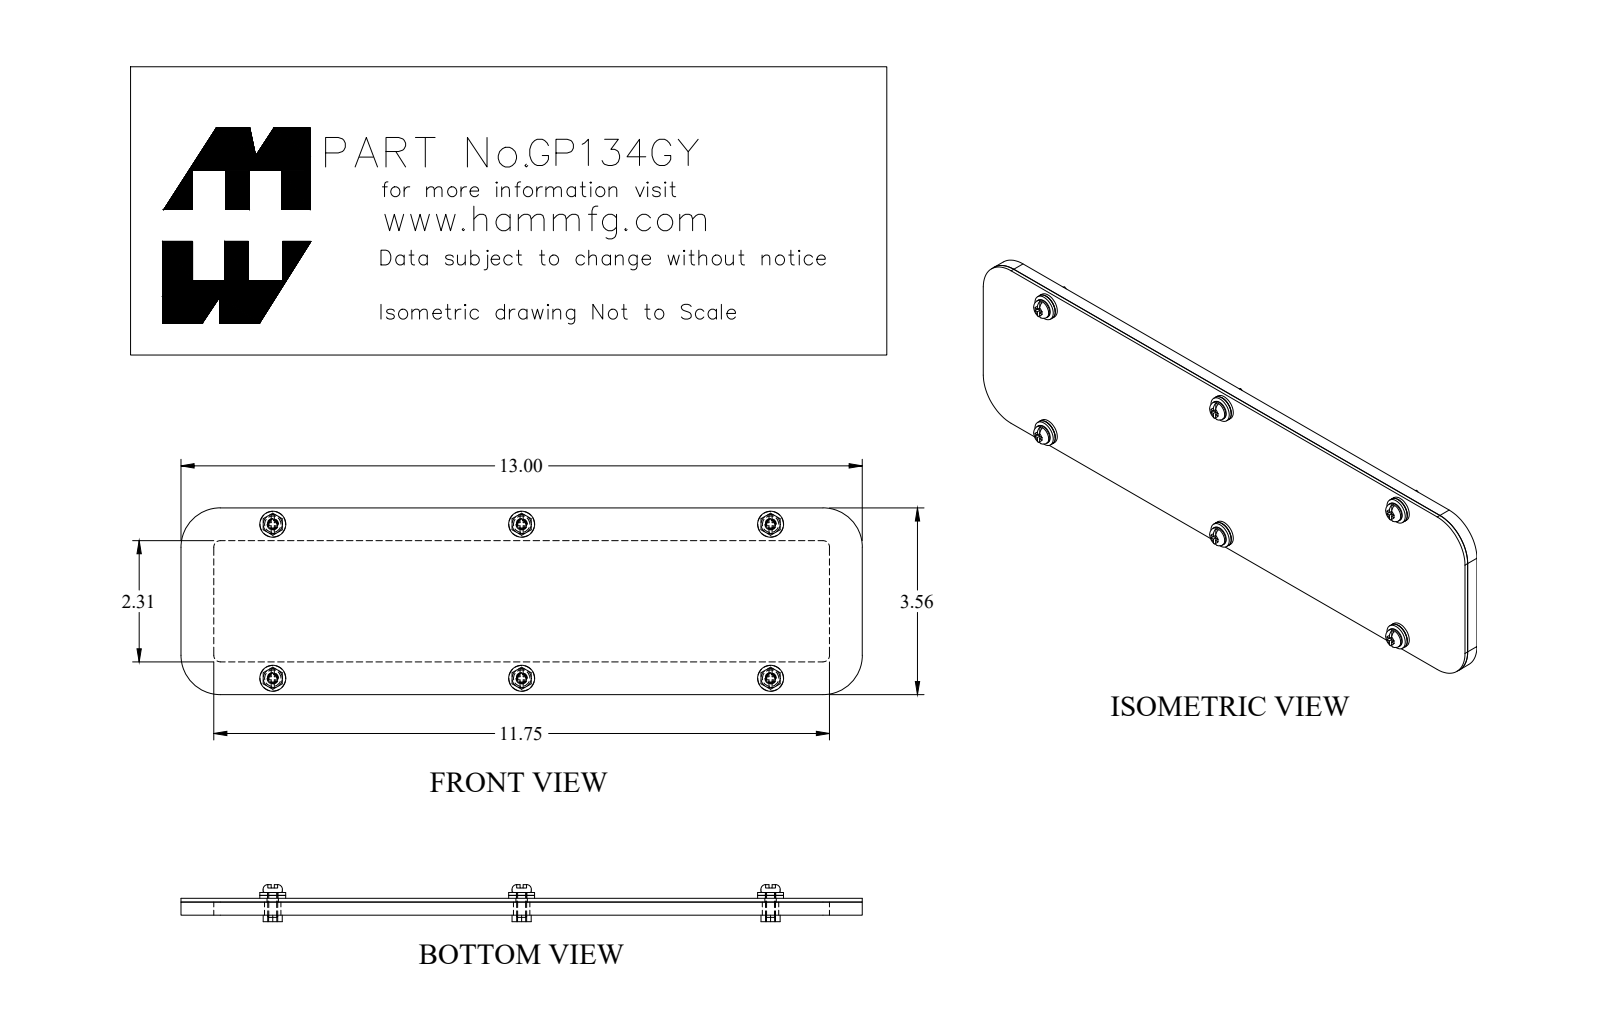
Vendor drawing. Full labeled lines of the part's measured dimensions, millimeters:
Part name (STEP PRODUCT): GP134GY
STEP written by: SolidWorks 2018 (AUTOMOTIVE_DESIGN)
Units: millimetres
Bodies: 20 solids, 346 faces (190 planar, 120 cylindrical, 36 other)
Overall size (bounding box): 330.2 × 90.5 × 18
Volume: 133 800 mm³ · Surface area: 100 900 mm²
Round holes (diameter × count): ⌀4 ×6, ⌀5 ×6, ⌀5.5 ×6, ⌀8 ×6
Round bosses / shafts (diameter × count): ⌀12.5 ×6, ⌀12.4 ×6, ⌀9.3 ×6, ⌀4.8 ×6
Partial cylindrical surfaces — rounded edges, fillets, slot ends (radius × count): R3.2 ×4, R19.1 ×4
Main face-to-face distances: 1.8, 8.2, 6.4, 15.9, 74.6, 90.5, 58.7, 2.8, 4.6, 11
Hole centre spacings: 120.7, 141.9, 241.3, 252.6, 74.6, 141.9, 74.6, 74.6
